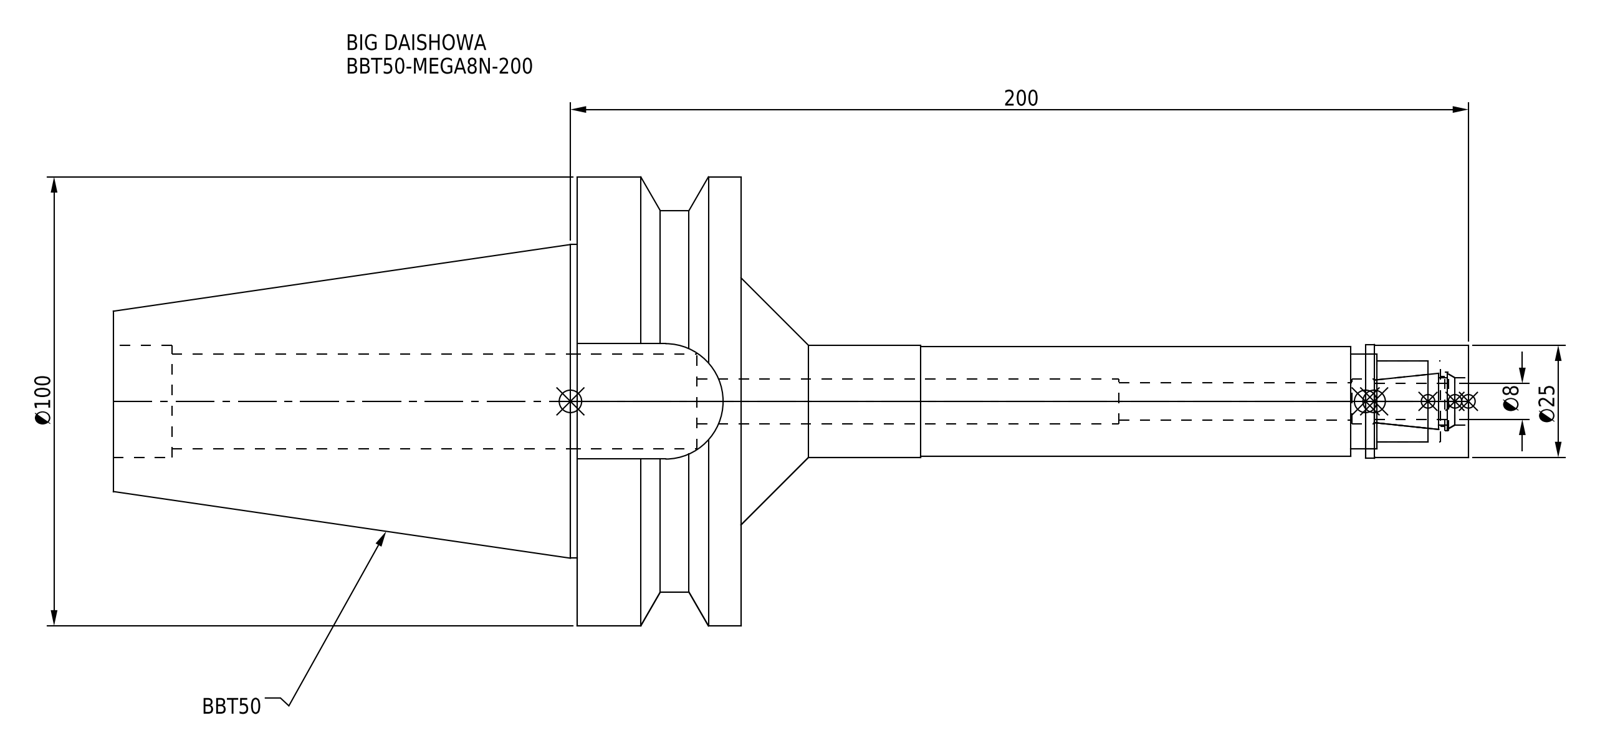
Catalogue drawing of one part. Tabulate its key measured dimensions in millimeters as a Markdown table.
| quantity | value |
| --- | --- |
| part name | BBT50-MEGA8N-200_1.stp; BBT50-MEGA8N-200; DXF_TEMP_ASSY_ASM_4_ASM.stp; BBT50-MEGA8N-200-080-FreeParts (+3 more) |
| STEP written by | SolidWorks 2019 (CONFIG_CONTROL_DESIGN) |
| units | millimeters |
| bodies | 2 solids, 82 faces (24 planar, 44 cylindrical, 14 other) |
| overall size | 301.8 × 100 × 100 |
| volume | 527 825 mm³ |
| surface area | 73 924 mm² |
| round holes (diameter × count) | 8.4 × 1, 10 × 1, 10.5 × 1, 11 × 1, 13 × 1, 18 × 1, 21 × 1, 21.2 × 1 |
| round bosses / shafts (diameter × count) | 100 × 1, 85 × 1, 69.85 × 1, 25.3 × 1, 25 × 1, 24.5 × 1 |
| partial cylindrical surfaces (radius × count) | 12.85 × 1 |
| main face-to-face distances | 36.5, 139.8, 103.3, 70.8, 25.7, 162, 198.5, 301.8, 171.8, 9.8 |
